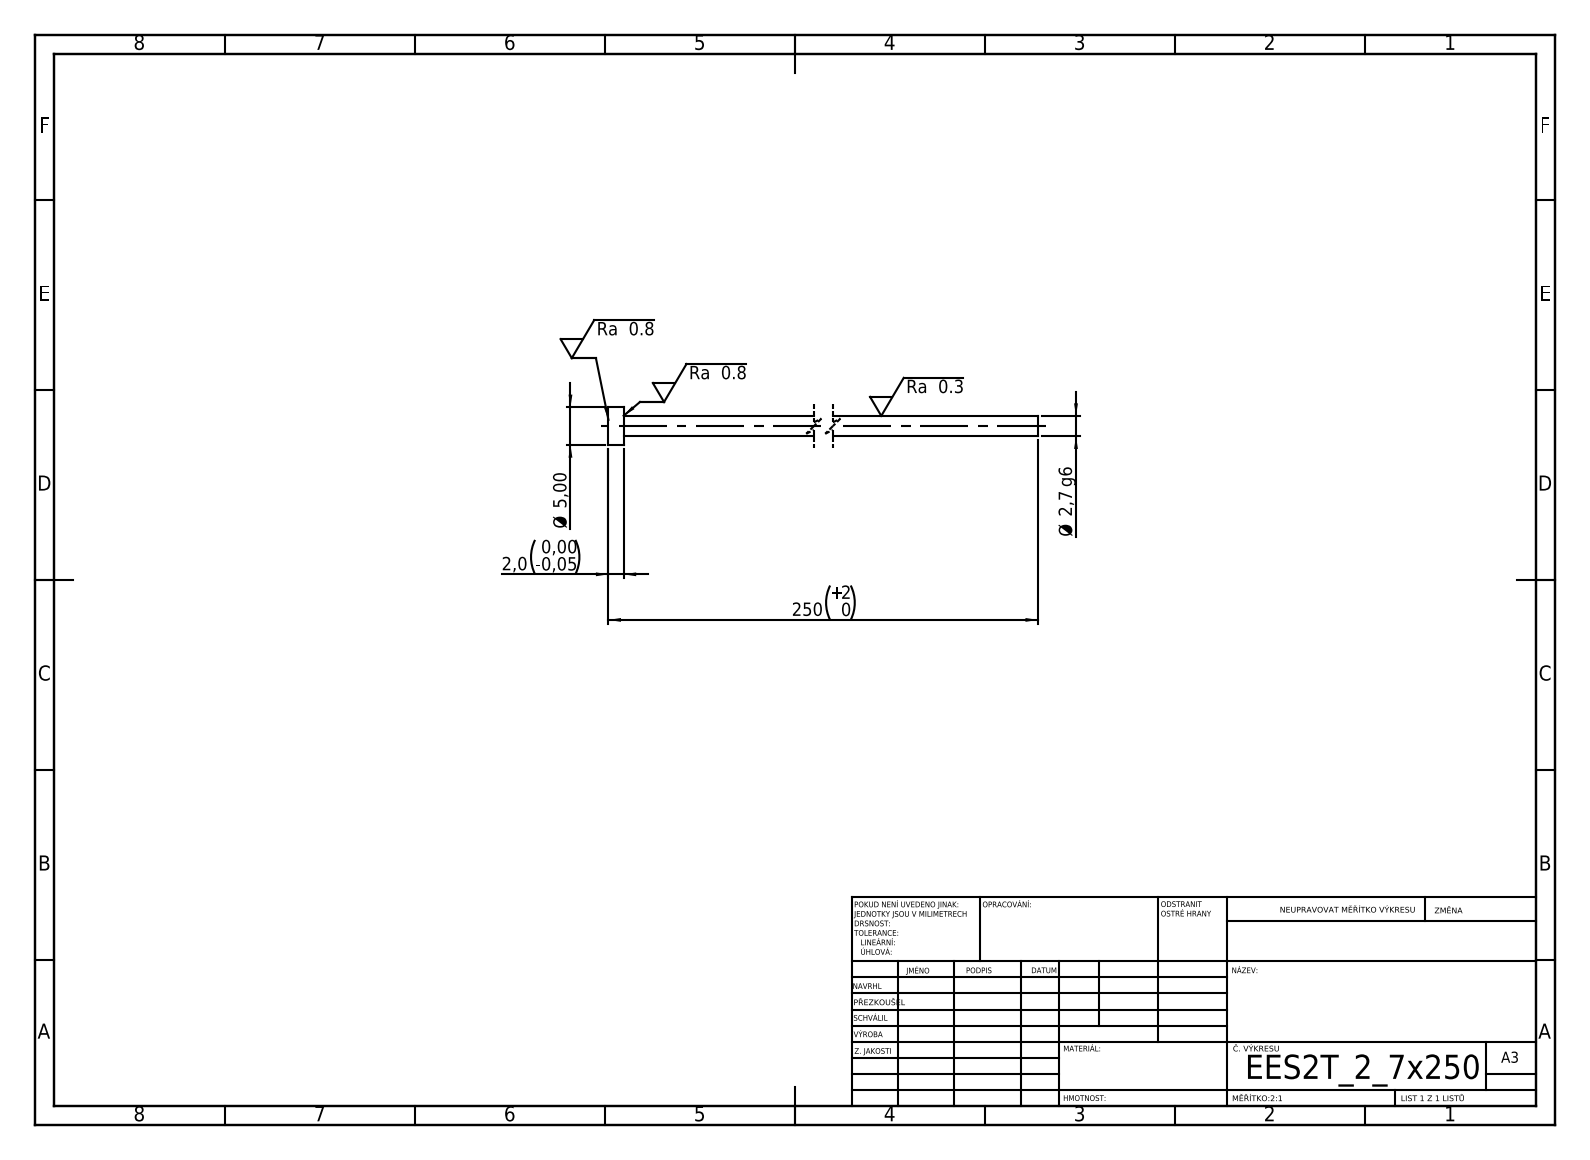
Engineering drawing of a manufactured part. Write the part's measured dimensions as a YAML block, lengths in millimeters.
step_written_by: "SolidWorks 2019 (CONFIG_CONTROL_DESIGN)"
units: millimeters
bodies: {solids: 1, faces: 7, planar: 3, cylindrical: 4, other: 0}
overall_size: [250, 5, 5]
volume: 1459
surface_area: 2174
round_bosses_or_shafts:
  - {diameter: 5, count: 1}
  - {diameter: 2.7, count: 1}
face_to_face_distances: [2, 250, 248]
